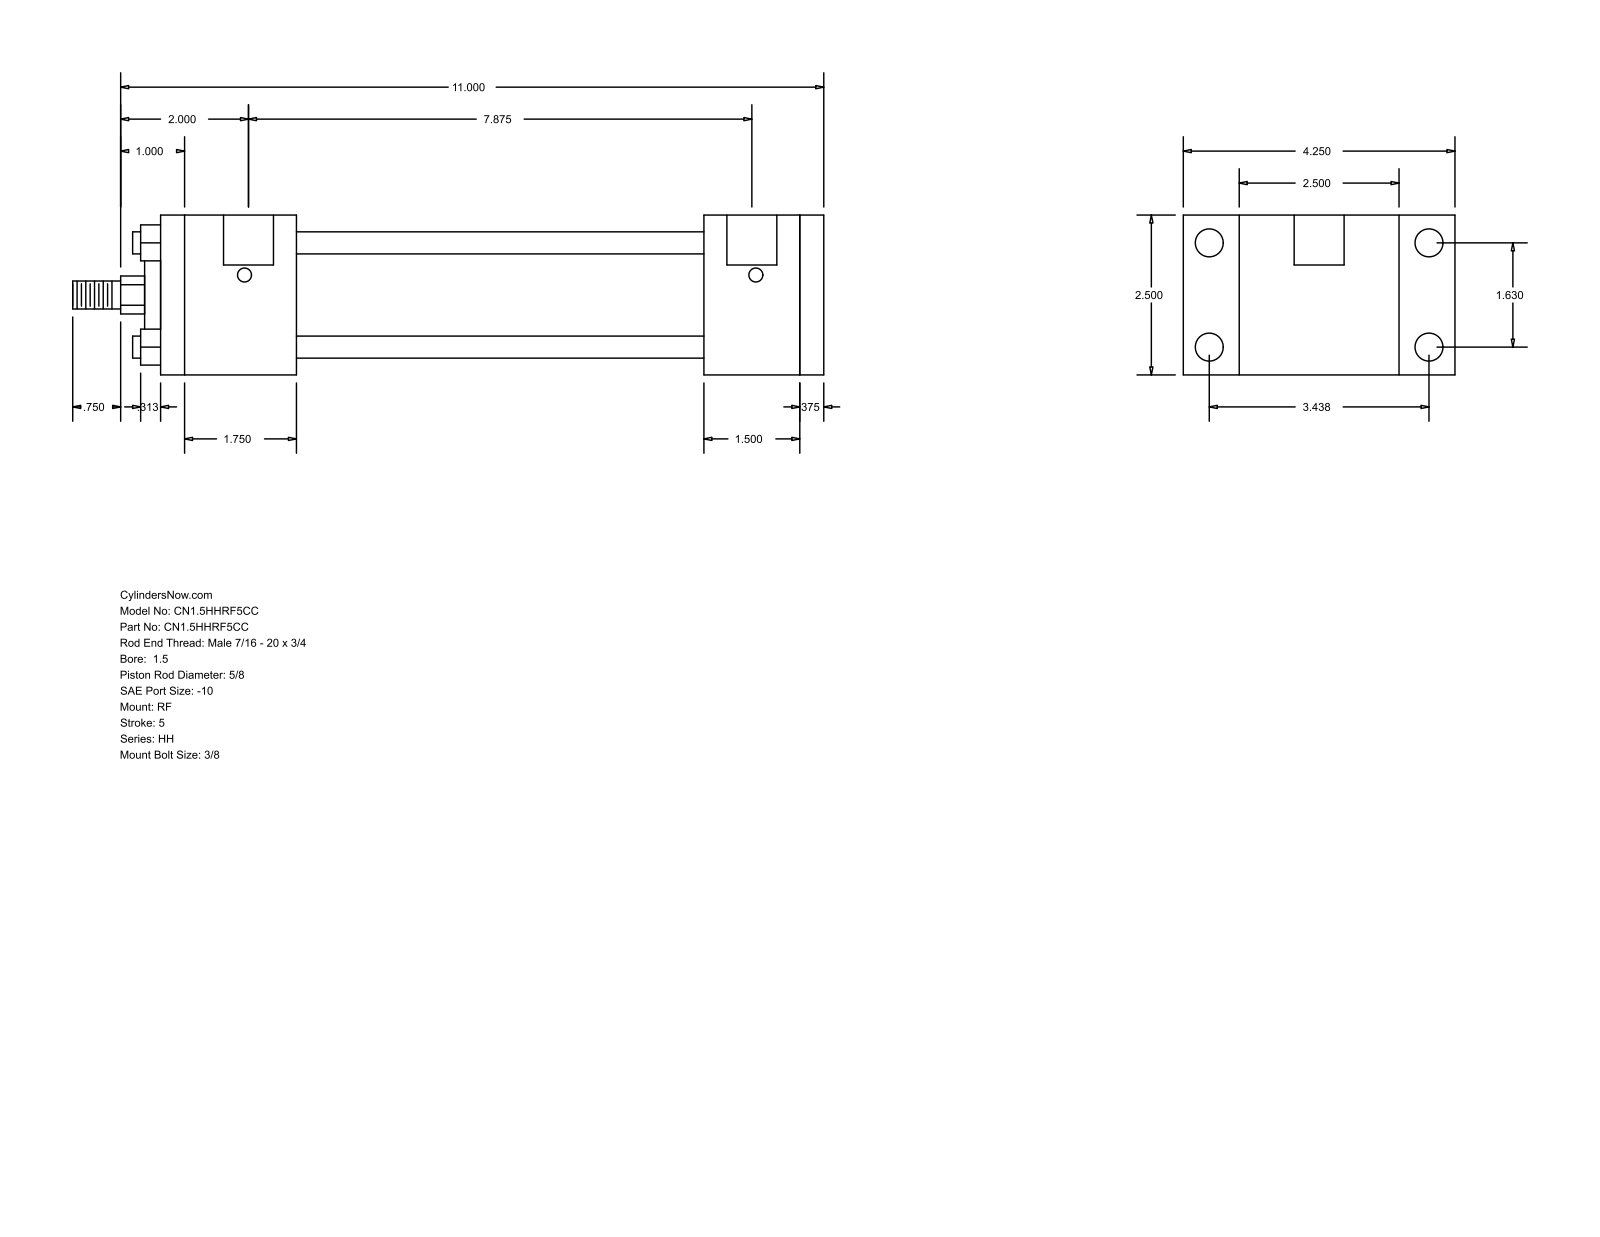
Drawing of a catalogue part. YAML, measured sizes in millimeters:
part_name: "HH_RF__0150_0.625"
step_written_by: "GSSL Pune (CONFIG_CONTROL_DESIGN)"
units: millimeters
bodies: {solids: 0, faces: 92, planar: 64, cylindrical: 28, other: 0}
overall_size: [298.45, 107.95, 63.5]
round_holes:
  - {diameter: 5.56, count: 4}
  - {diameter: 11.13, count: 4}
  - {diameter: 19.84, count: 2}
round_bosses_or_shafts:
  - {diameter: 8.76, count: 4}
  - {diameter: 44.45, count: 1}
  - {diameter: 28.57, count: 1}
  - {diameter: 15.88, count: 1}
  - {diameter: 11.11, count: 1}
partial_cylinders:
  - {radius: 7.54, count: 1}
face_to_face_distances: [63.5, 263.52, 38.1, 254, 9.52, 53.97, 215.9, 161.93, 200.03, 209.55]
hole_center_spacings: [1.59, 41.4, 87.32, 96.64, 201.61, 203.2, 200.02]
